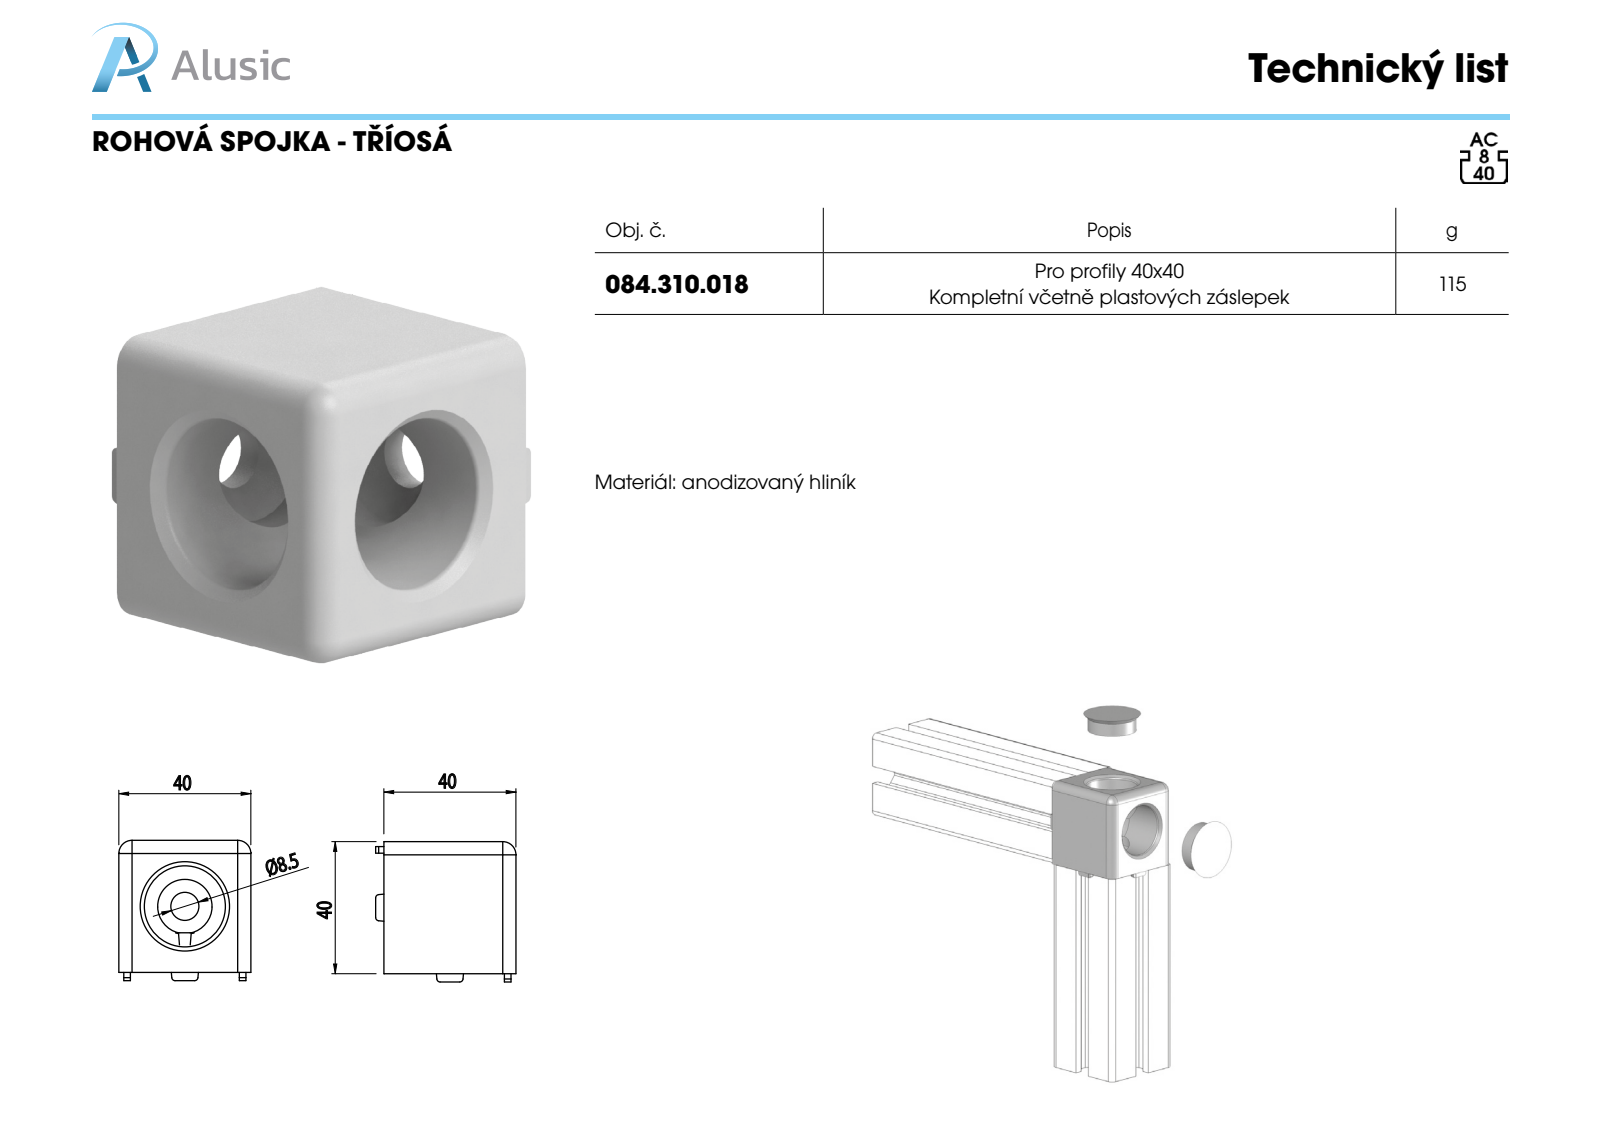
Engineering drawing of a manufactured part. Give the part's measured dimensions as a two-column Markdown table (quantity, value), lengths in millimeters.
| quantity | value |
| --- | --- |
| part name | 084.310.018 |
| STEP written by | SolidWorks 2011 (CONFIG_CONTROL_DESIGN) |
| units | millimeters |
| bodies | 1 solid, 90 faces (40 planar, 25 cylindrical, 25 other) |
| overall size | 42.5 × 42.5 × 40 |
| volume | 42 560 mm³ |
| surface area | 11 909 mm² |
| round holes (diameter × count) | 8.5 × 2 |
| partial cylindrical surfaces (radius × count) | 1 × 12, 4 × 5 |
| main face-to-face distances | 40, 14.75, 25.25, 12, 28, 10.5, 36.5, 3.5, 38.5, 1.5 |
